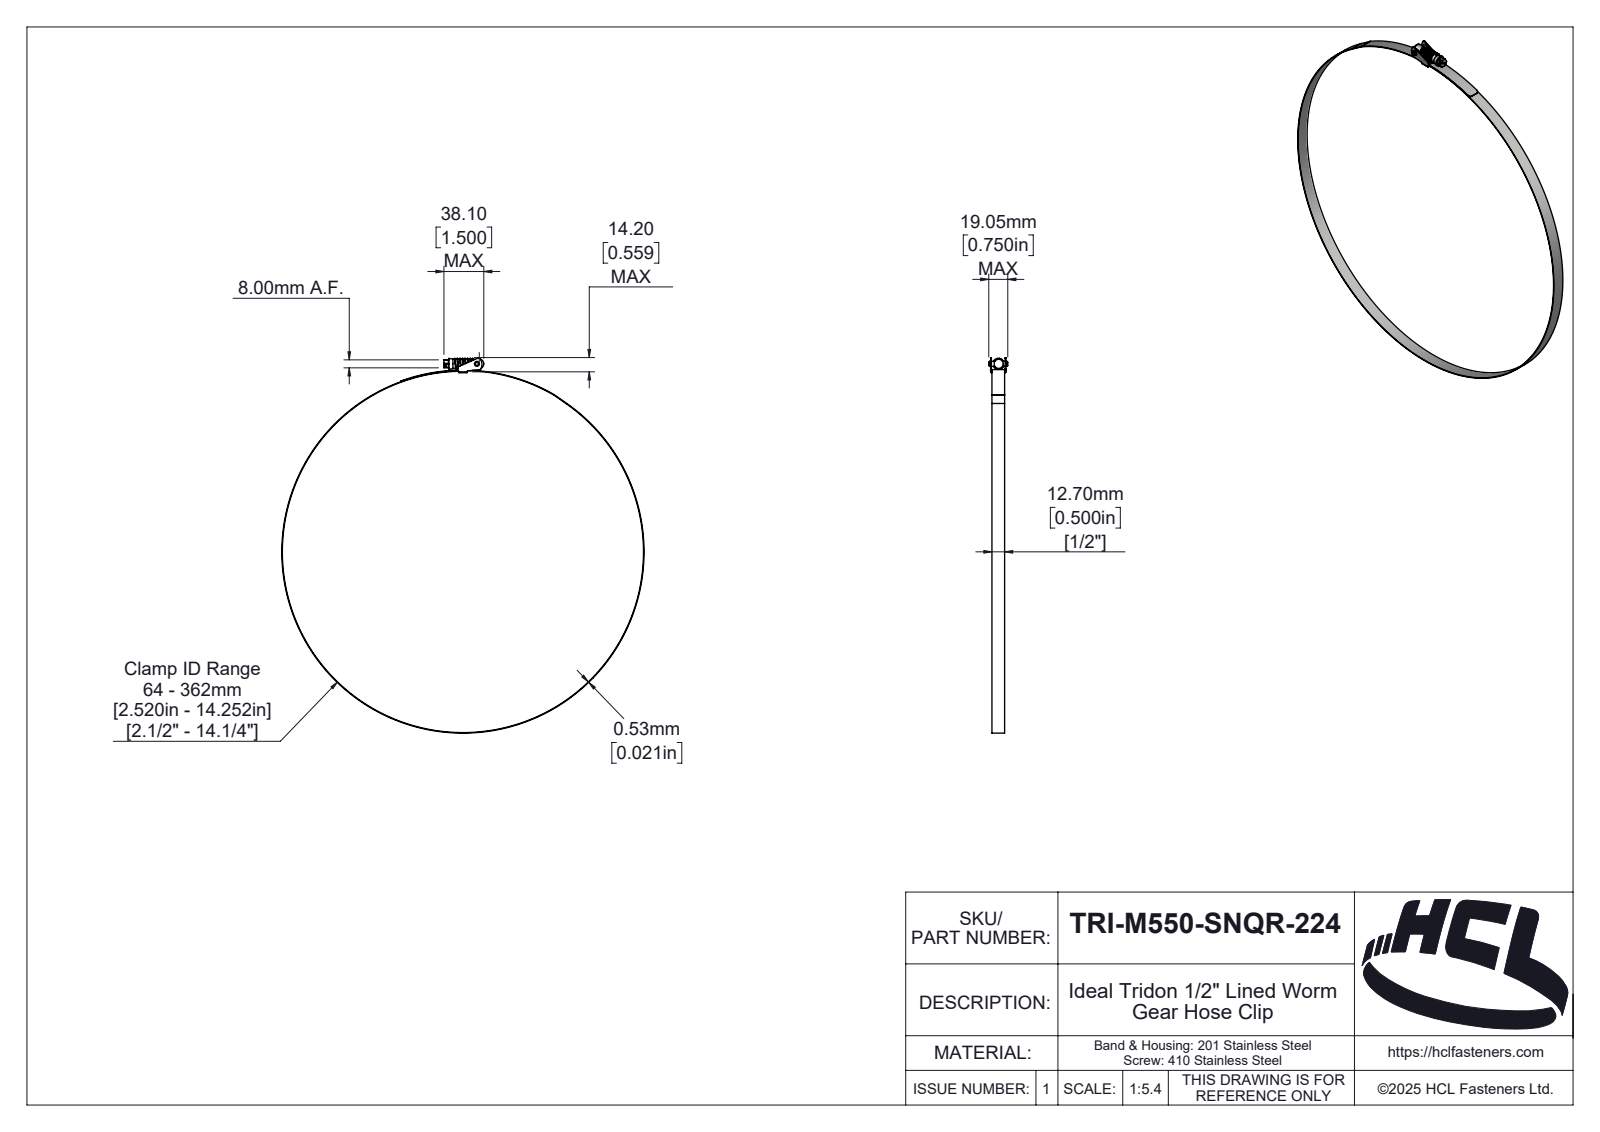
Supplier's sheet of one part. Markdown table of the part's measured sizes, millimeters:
| quantity | value |
| --- | --- |
| part name | TRI-M550-SNQR-224 |
| STEP written by | SolidWorks 2025 (AUTOMOTIVE_DESIGN) |
| units | millimeters |
| bodies | 5 solids, 222 faces (44 planar, 112 cylindrical, 66 other) |
| overall size | 376.02 × 363.06 × 19.05 |
| volume | 11 274 mm³ |
| surface area | 35 408 mm² |
| round holes (diameter × count) | 5 × 1, 362 × 1 |
| round bosses / shafts (diameter × count) | 363.06 × 1, 9.1 × 1 |
| partial cylindrical surfaces (radius × count) | 1 × 11, 0.1 × 2, 0.9 × 2, 3 × 2, 0.46 × 1, 1.89 × 1, 2 × 1, 2.35 × 1 |
| main face-to-face distances | 12.7, 0.8, 1.35, 14.05, 14.6, 0.55, 13.25, 0.53, 15.4, 13.8 |
| hole center spacings | 188.92 |
